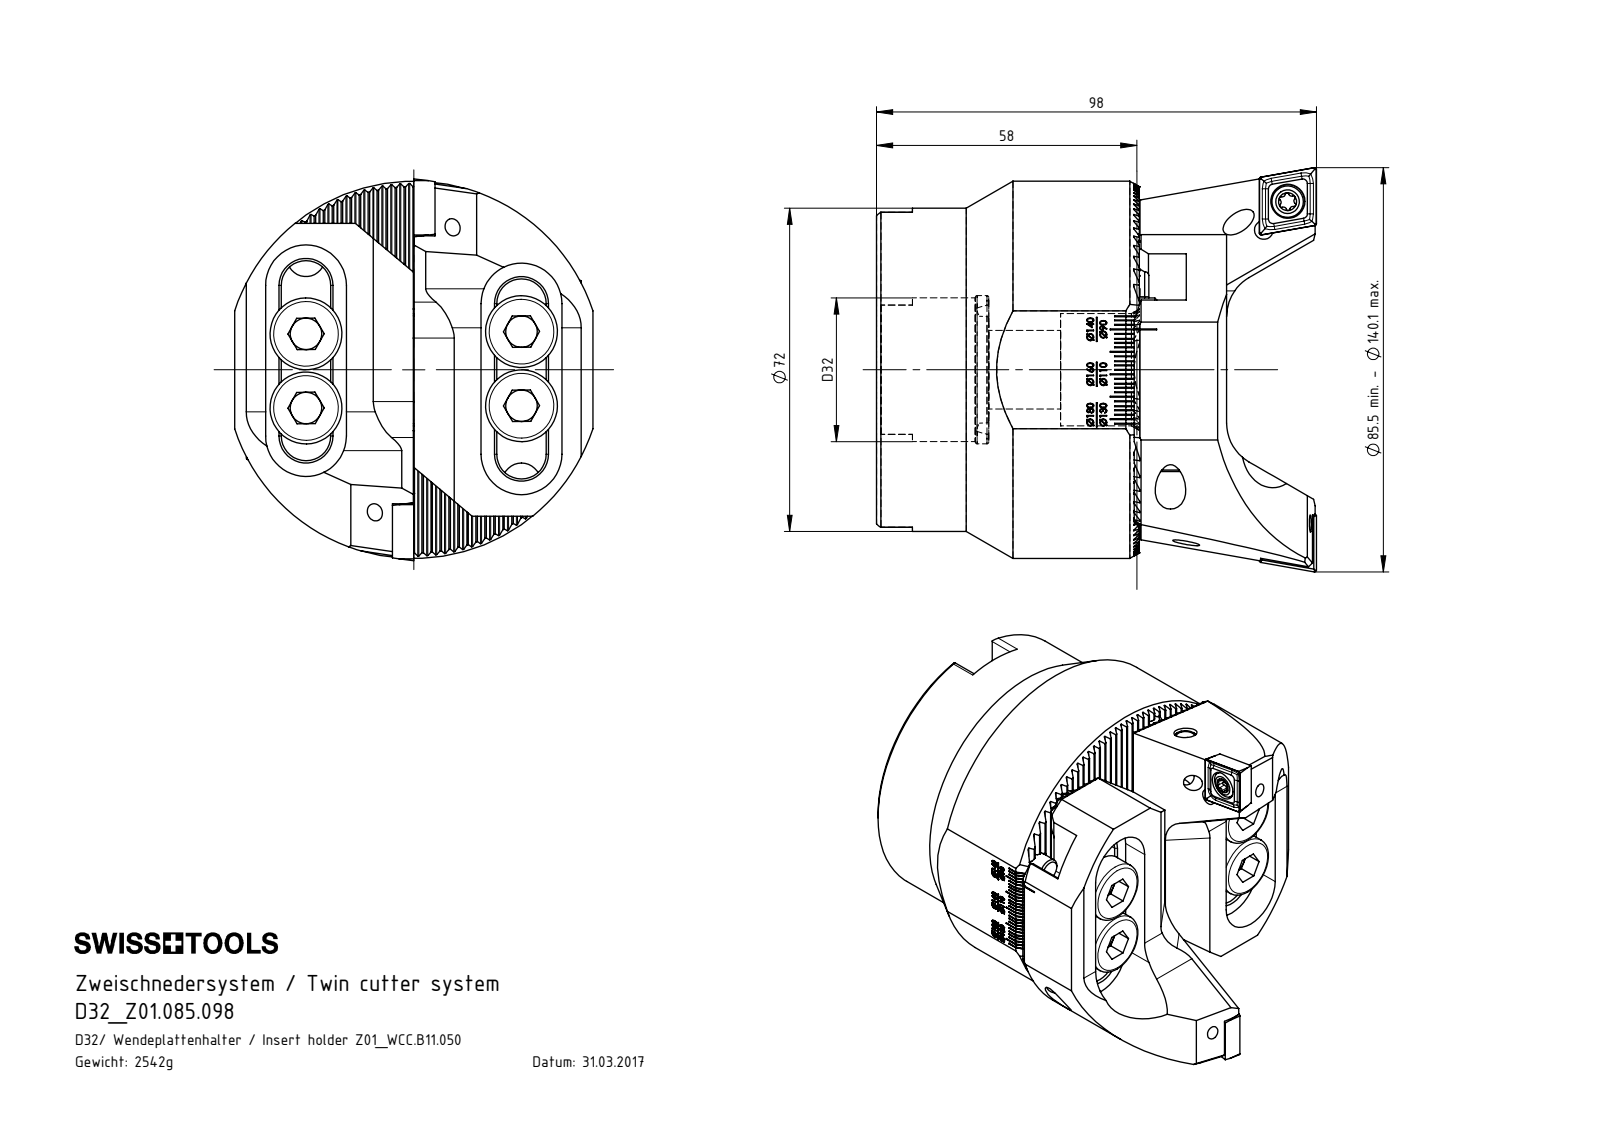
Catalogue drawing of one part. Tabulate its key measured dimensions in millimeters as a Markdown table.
| quantity | value |
| --- | --- |
| part name | CCMT120404; WCC-ER2.001.010_A; ISO 4026 - M6 x 6; Z01-WCC.B11.050_A_mit beschriftung (+8 more) |
| STEP written by | SolidWorks 2017 (AUTOMOTIVE_DESIGN) |
| units | millimeters |
| bodies | 22 solids, 2317 faces (1464 planar, 282 cylindrical, 571 other) |
| overall size | 98 × 90.01 × 79.8 |
| volume | 335 479 mm³ |
| surface area | 79 963 mm² |
| round holes (diameter × count) | 5 × 10, 8.5 × 8, 4.2 × 6, 6.5 × 6, 3.3 × 2, 5.5 × 2, 6 × 2, 6.8 × 2, 7.6 × 2, 17.5 × 1, 25 × 1, 32 × 1 |
| round bosses / shafts (diameter × count) | 6 × 6, 16 × 5, 10 × 4, 7 × 2, 5 × 2, 84 × 1, 72 × 1, 24 × 1 |
| partial cylindrical surfaces (radius × count) | 0.14 × 79, 0.39 × 12, 5.5 × 8, 0.69 × 6, 0.69 × 6, 0.8 × 4, 1 × 4, 2.5 × 4 |
| main face-to-face distances | 1.73, 8.66, 6.93, 40, 5.2, 15.59, 10.39, 13.86, 3.46, 17.32 |
| hole center spacings | 16.5, 34.66, 41.56, 48, 50.92, 8.21, 8.33, 9 |
